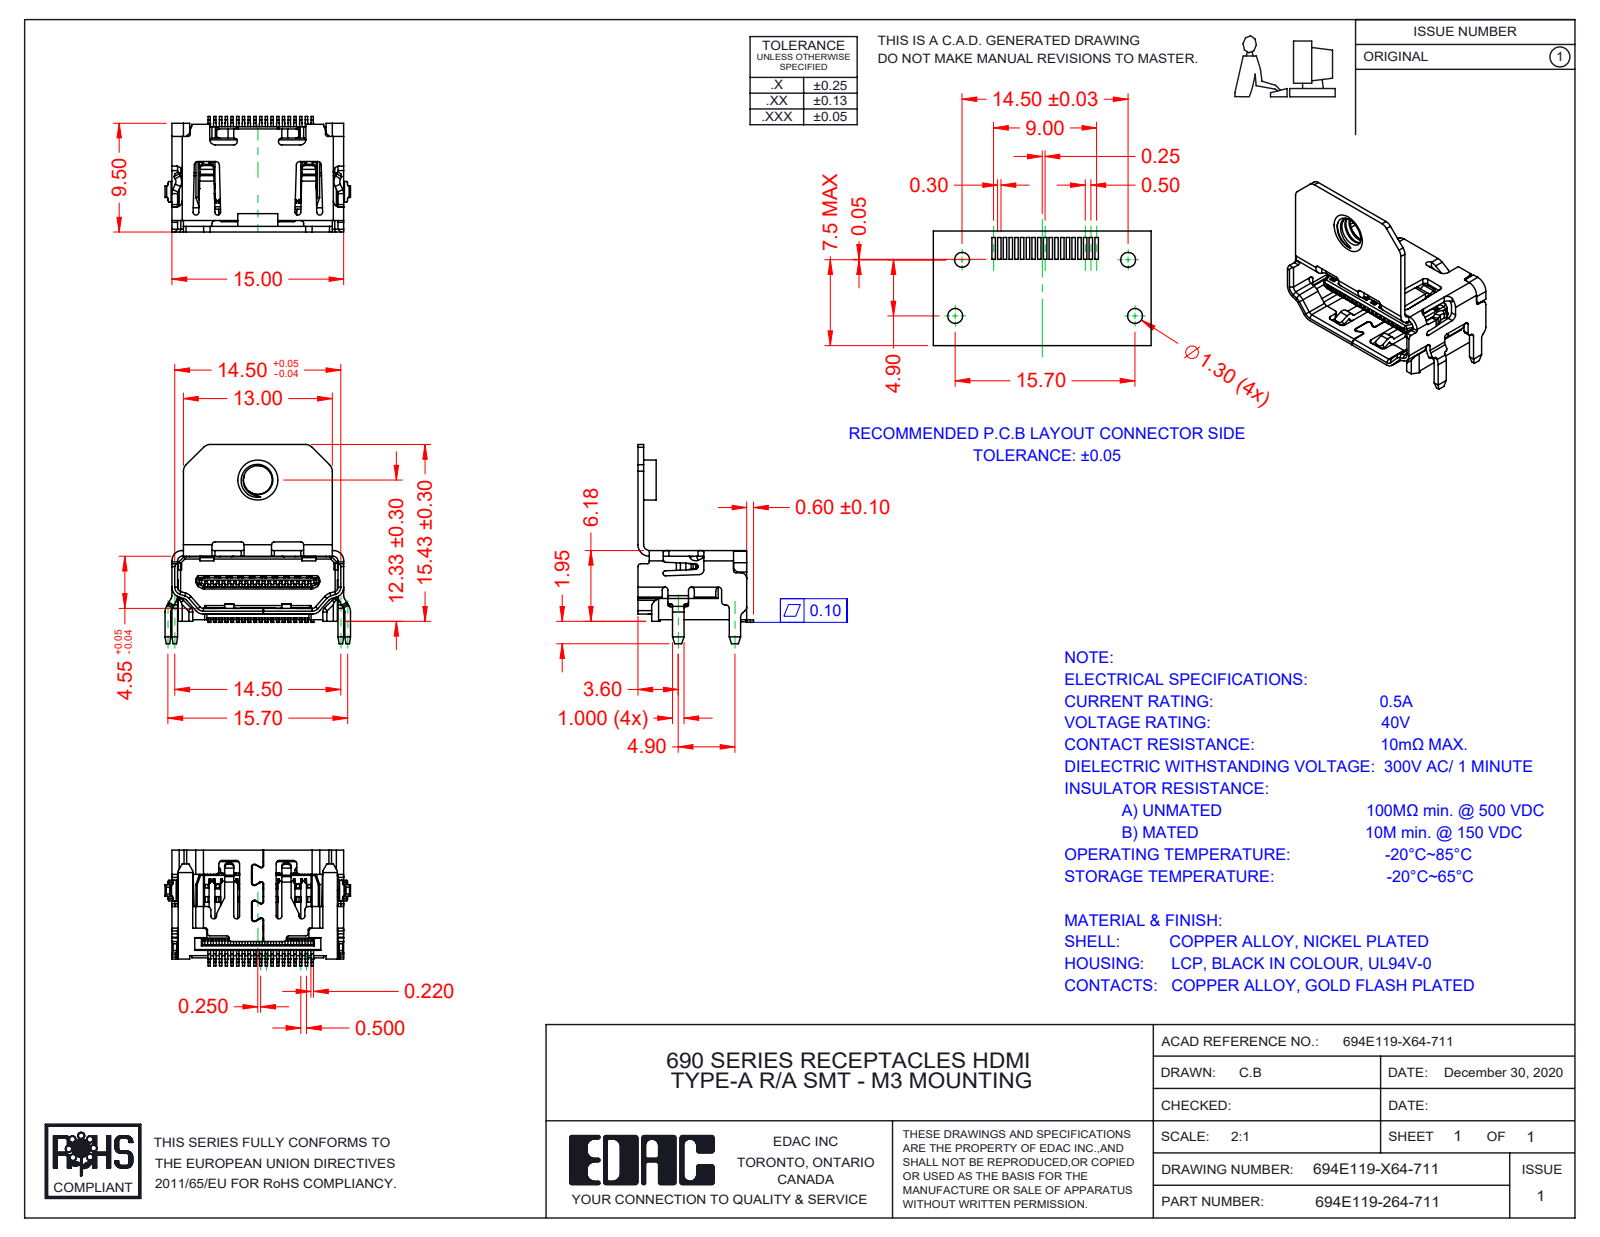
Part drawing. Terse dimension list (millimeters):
name: Contact Lower 694E119-X64-711; 694E119-164-711; Contact Upper 694E119-X64-711; Insulator 694E119-X64-711 (+1 more)
written by: SolidWorks 2020 (AUTOMOTIVE_DESIGN)
unit: mm
bodies: 21 solids, 2744 faces (1991 planar, 676 cylindrical, 77 other)
size: 17.38 × 16.2 × 10.1
volume: 399 mm³; area: 1 675 mm²
holes: 1× ⌀2.5
bosses: 1× ⌀3.5
rounds: 47× R0.2, 32× R0.25, 26× R0.3, 24× R0.5, 23× R0.15, 13× R1, 10× R0.4, 8× R0.35
face distances: 0.5, 2.52, 2.02, 5.04, 3.02, 8.7, 9.2, 0.55, 2.4, 6.3
